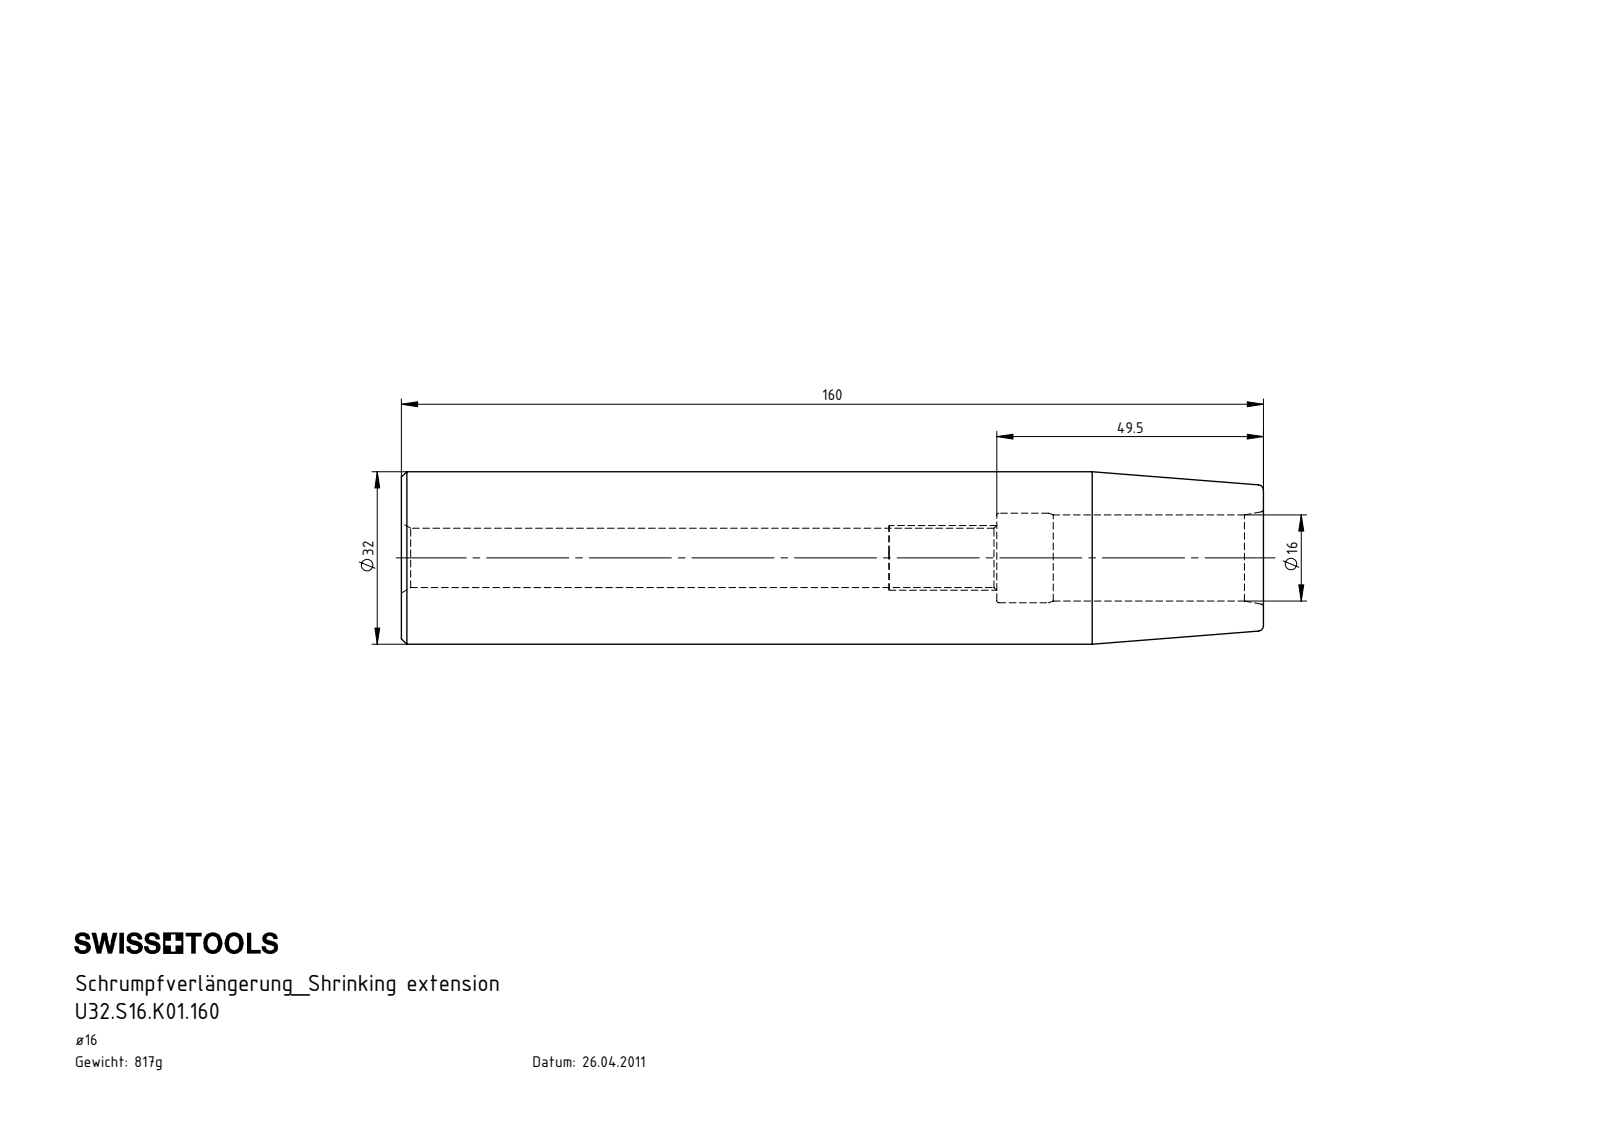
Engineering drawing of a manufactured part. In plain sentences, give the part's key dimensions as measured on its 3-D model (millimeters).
The part is named "U32.S16.K01.160". Its 3-D file was written by "SolidWorks 2017 (AUTOMOTIVE_DESIGN)". It is 1 solid with 31 faces: 3 planar, 8 cylindrical and 20 other. Overall it measures 160 by 32 by 32 millimeters. Its volume is 104 131 cubic millimeters and its surface area 23 213 square millimeters. Round holes: 1 of diameter 11, 1 of diameter 16, 1 of diameter 16.6. Round bosses or shafts: 1 of diameter 32. The main face-to-face distances are 160, 110.5, 49.5.
